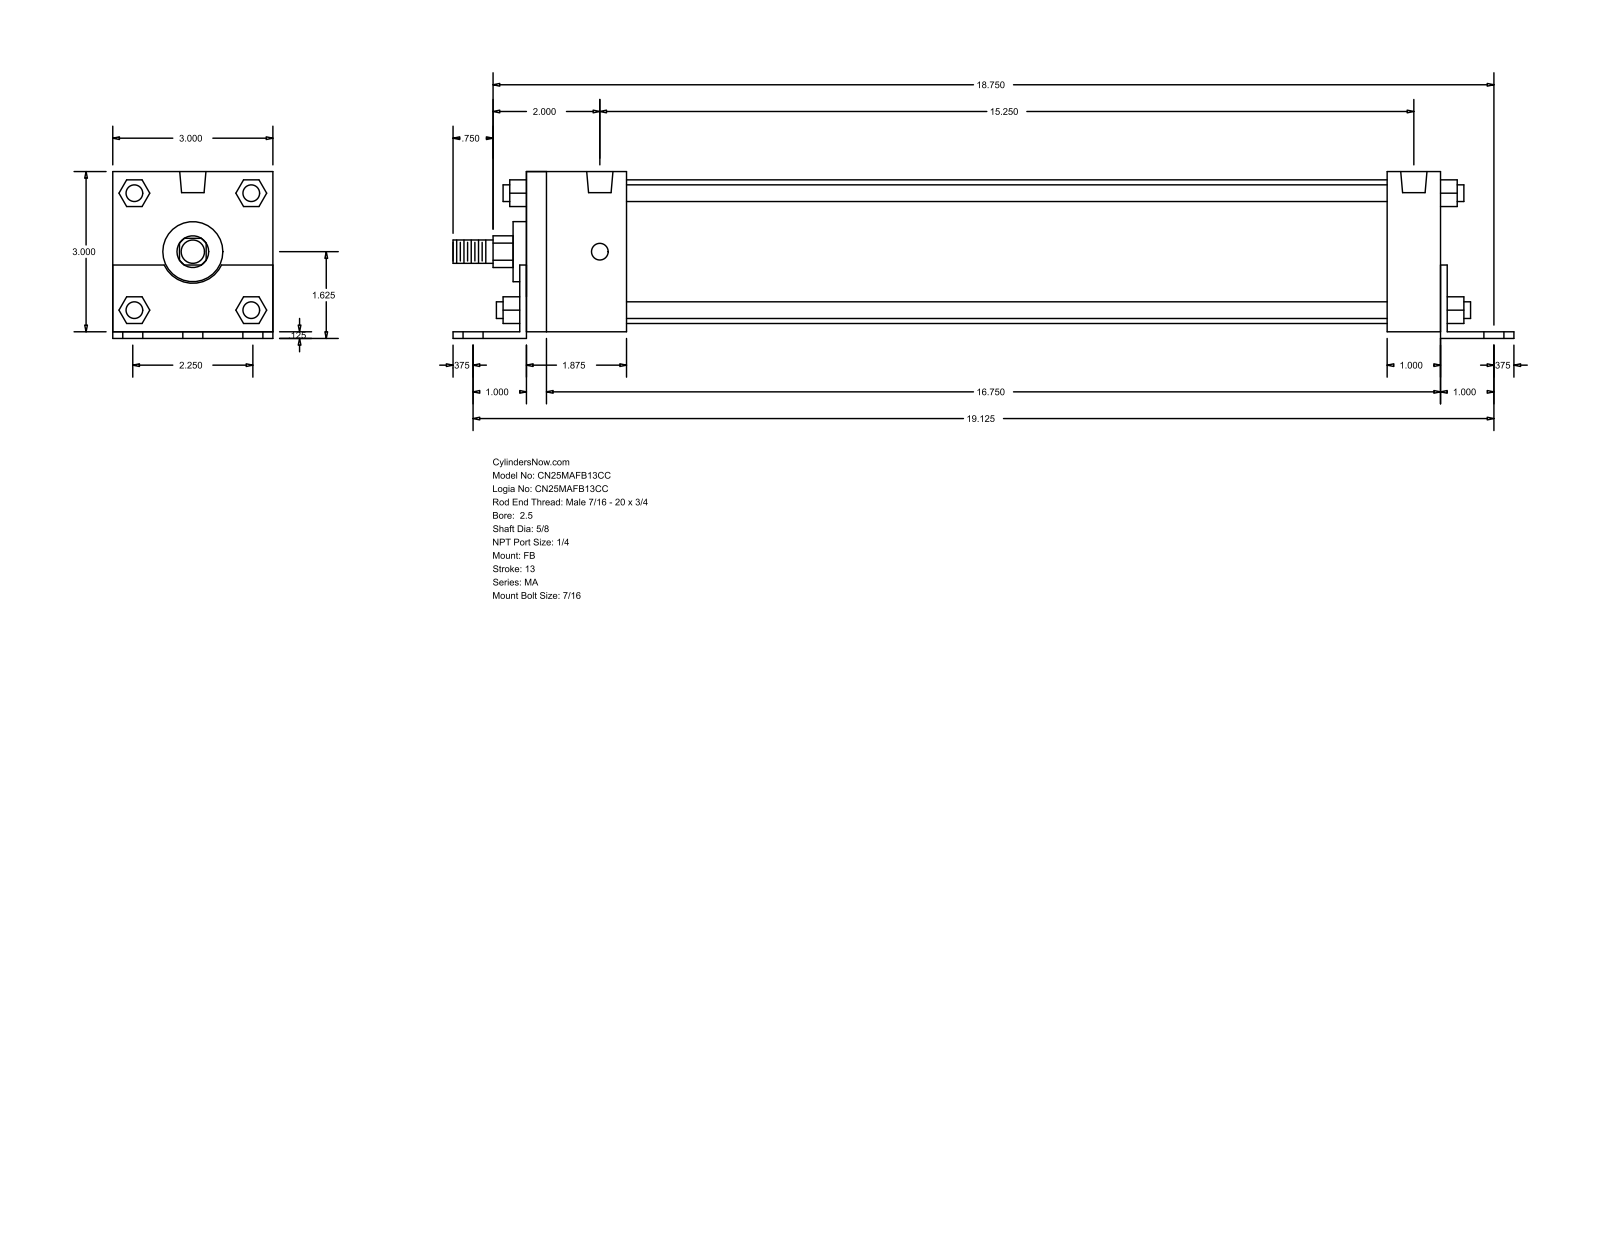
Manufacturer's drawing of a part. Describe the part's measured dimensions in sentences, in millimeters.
The part is named "MA_FB__0250_0.625". Its 3-D file was written by "GSSL Pune (CONFIG_CONTROL_DESIGN)". It is 0 solids with 140 faces: 105 planar, 35 cylindrical and 0 other. Overall it measures 504.82 by 79.38 by 76.2 millimeters. Round holes: 6 of diameter 11.11, 4 of diameter 7.94, 2 of diameter 12.49. Round bosses or shafts: 4 of diameter 7.94, 1 of diameter 68.33, 1 of diameter 28.57, 1 of diameter 15.88, 1 of diameter 11.11. Partial cylindrical surfaces (rounded edges, fillets, slot ends): 1 of radius 7.54, 1 of radius 15.05. The main face-to-face distances are 76.2, 3.17, 79.37, 434.97, 441.32, 3.18, 438.14, 47.62, 25.4, 438.15. The hole center spacings are 28.57, 486.62, 485.78, 47.62, 57.14, 66.75, 387.35, 426.41.
